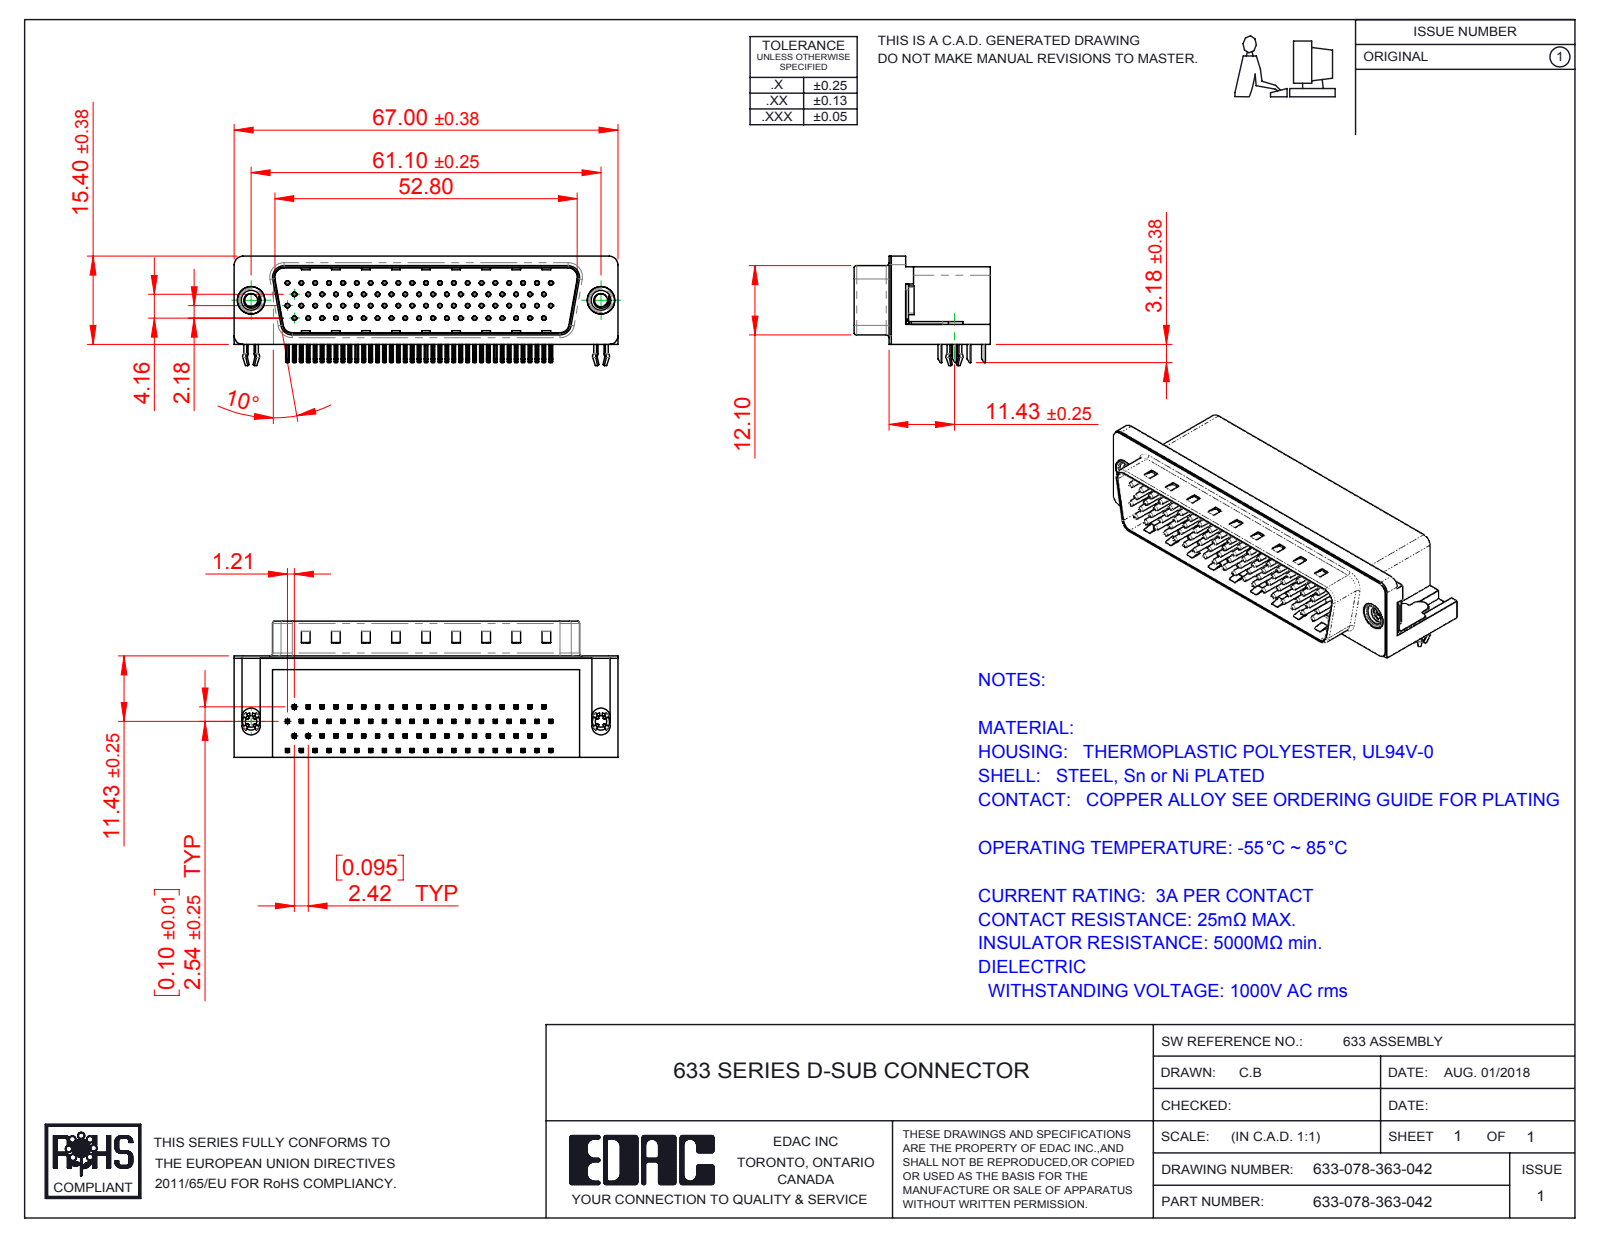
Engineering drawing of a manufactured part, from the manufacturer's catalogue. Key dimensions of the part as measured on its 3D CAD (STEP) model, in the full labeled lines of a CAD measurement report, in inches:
Part name (STEP PRODUCT): 633 Contact Bottom_78 Contact; 633 Contact Top 78; 633 4 Prong Board Lock_78 Contact; 633 4-40 Threaded Rivet (+5 more)
STEP written by: SolidWorks 2016 (CONFIG_CONTROL_DESIGN)
Units: inches
Bodies: 84 solids, 6396 faces (4023 planar, 1784 cylindrical, 589 other)
Overall size (bounding box): 2.638 × 0.937 × 0.752
Volume: 0.892 in³ · Surface area: 25.47 in²
Round holes (diameter × count): ⌀0.014 ×78, ⌀0.031 ×78, ⌀0.079 ×2, ⌀0.089 ×2, ⌀0.157 ×2, ⌀0.189 ×2, ⌀0.197 ×2
Round bosses / shafts (diameter × count): ⌀0.03 ×78, ⌀0.193 ×2, ⌀0.187 ×2, ⌀0.154 ×2, ⌀0.118 ×2
Partial cylindrical surfaces — rounded edges, fillets, slot ends (radius × count): R0.01 ×324, R0.005 ×156, R0.039 ×16, R0.02 ×9, R0.063 ×8, R0.059 ×6, R0.018 ×4, R0.035 ×4
Main face-to-face distances: 0.016, 0.52, 0.681, 0.461, 0.526, 0.081, 0.541, 0.065, 0.073, 0.469
Hole centre spacings: 0.095, 0.191, 0.286, 0.381, 0.246, 0.281, 0.476, 0.339
